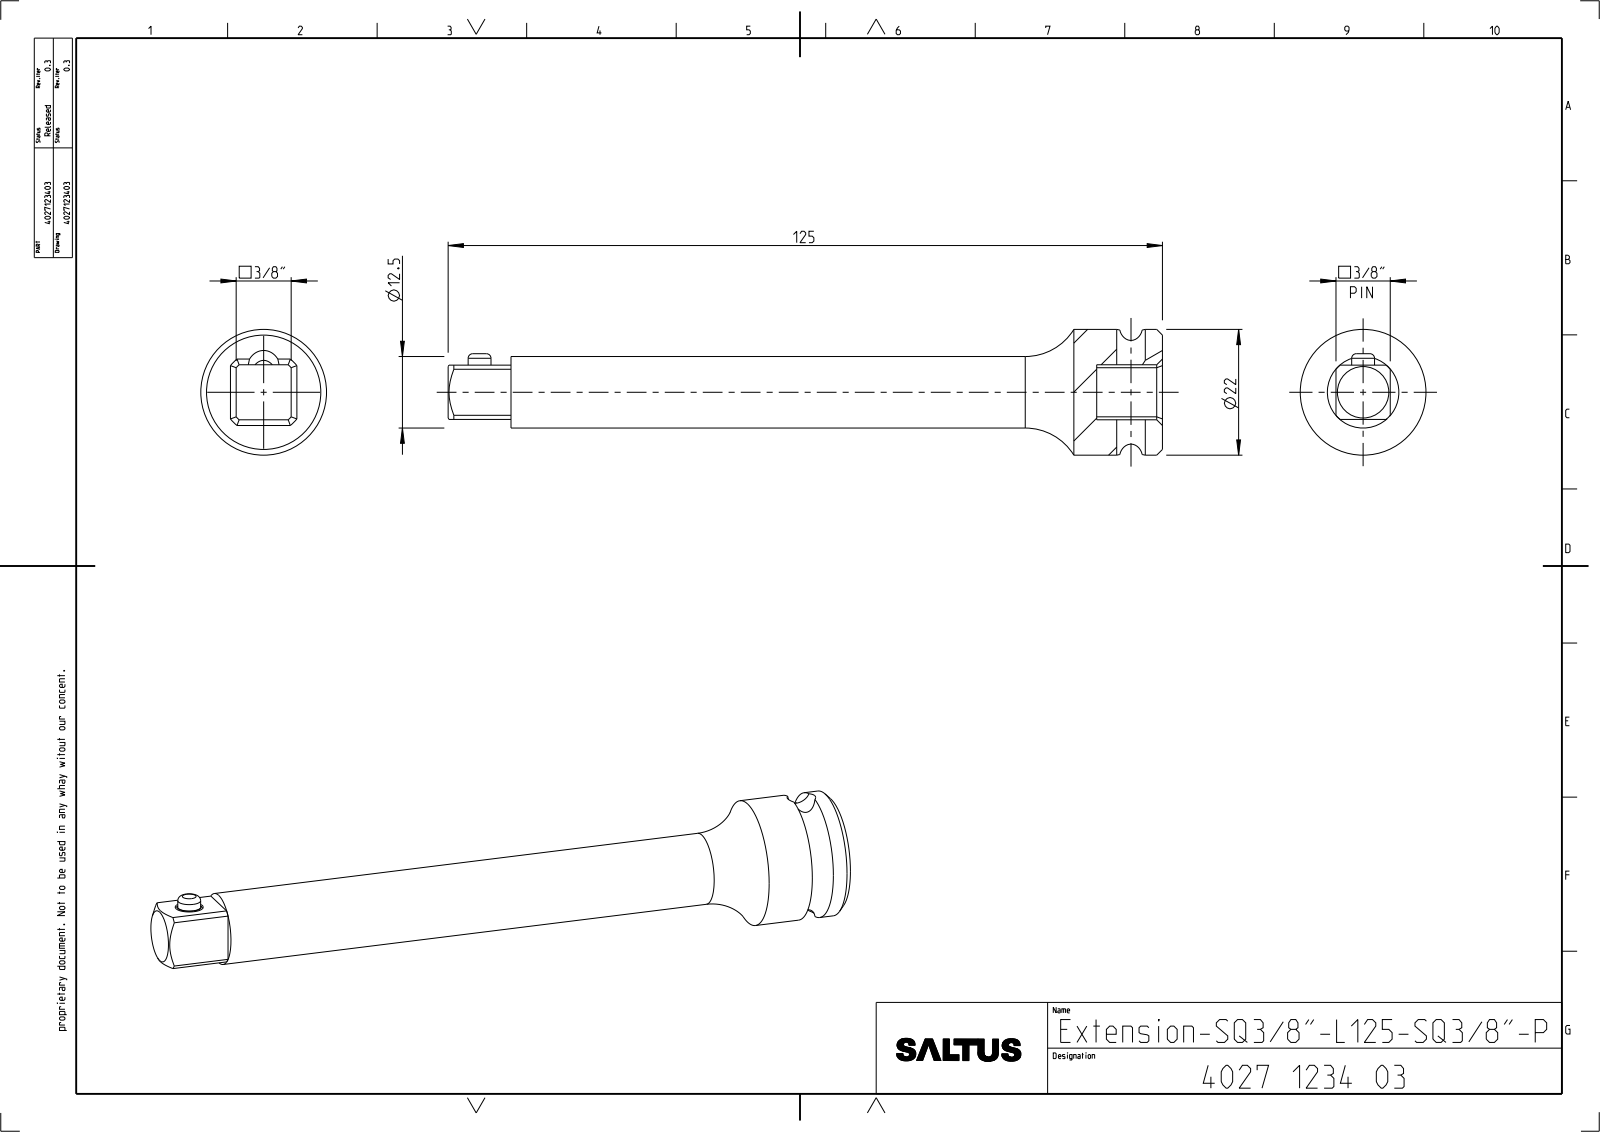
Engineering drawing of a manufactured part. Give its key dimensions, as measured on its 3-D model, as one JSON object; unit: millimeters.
{"part_name": "4027123403", "step_written_by": "CREO PARAMETRIC BY PTC INC, 2022414 (CONFIG_CONTROL_DESIGN)", "units": "millimeters", "bodies": {"solids": 2, "faces": 65, "planar": 22, "cylindrical": 25, "other": 18}, "overall_size": [125, 22, 22], "volume_mm3": 17873, "surface_area_mm2": 6761, "round_holes": [[4.9, 1], [5, 1]], "round_bosses_or_shafts": [[22, 1], [12.51, 1], [4.8, 1], [4, 1]], "partial_cylinders_radius": [[3, 1], [6.22, 1], [6.45, 1]], "face_to_face_distances": [9.56, 9.5, 9.62, 11.5, 125, 113.5, 114, 102.5, 11, 3.25], "hole_center_spacings": [114]}
